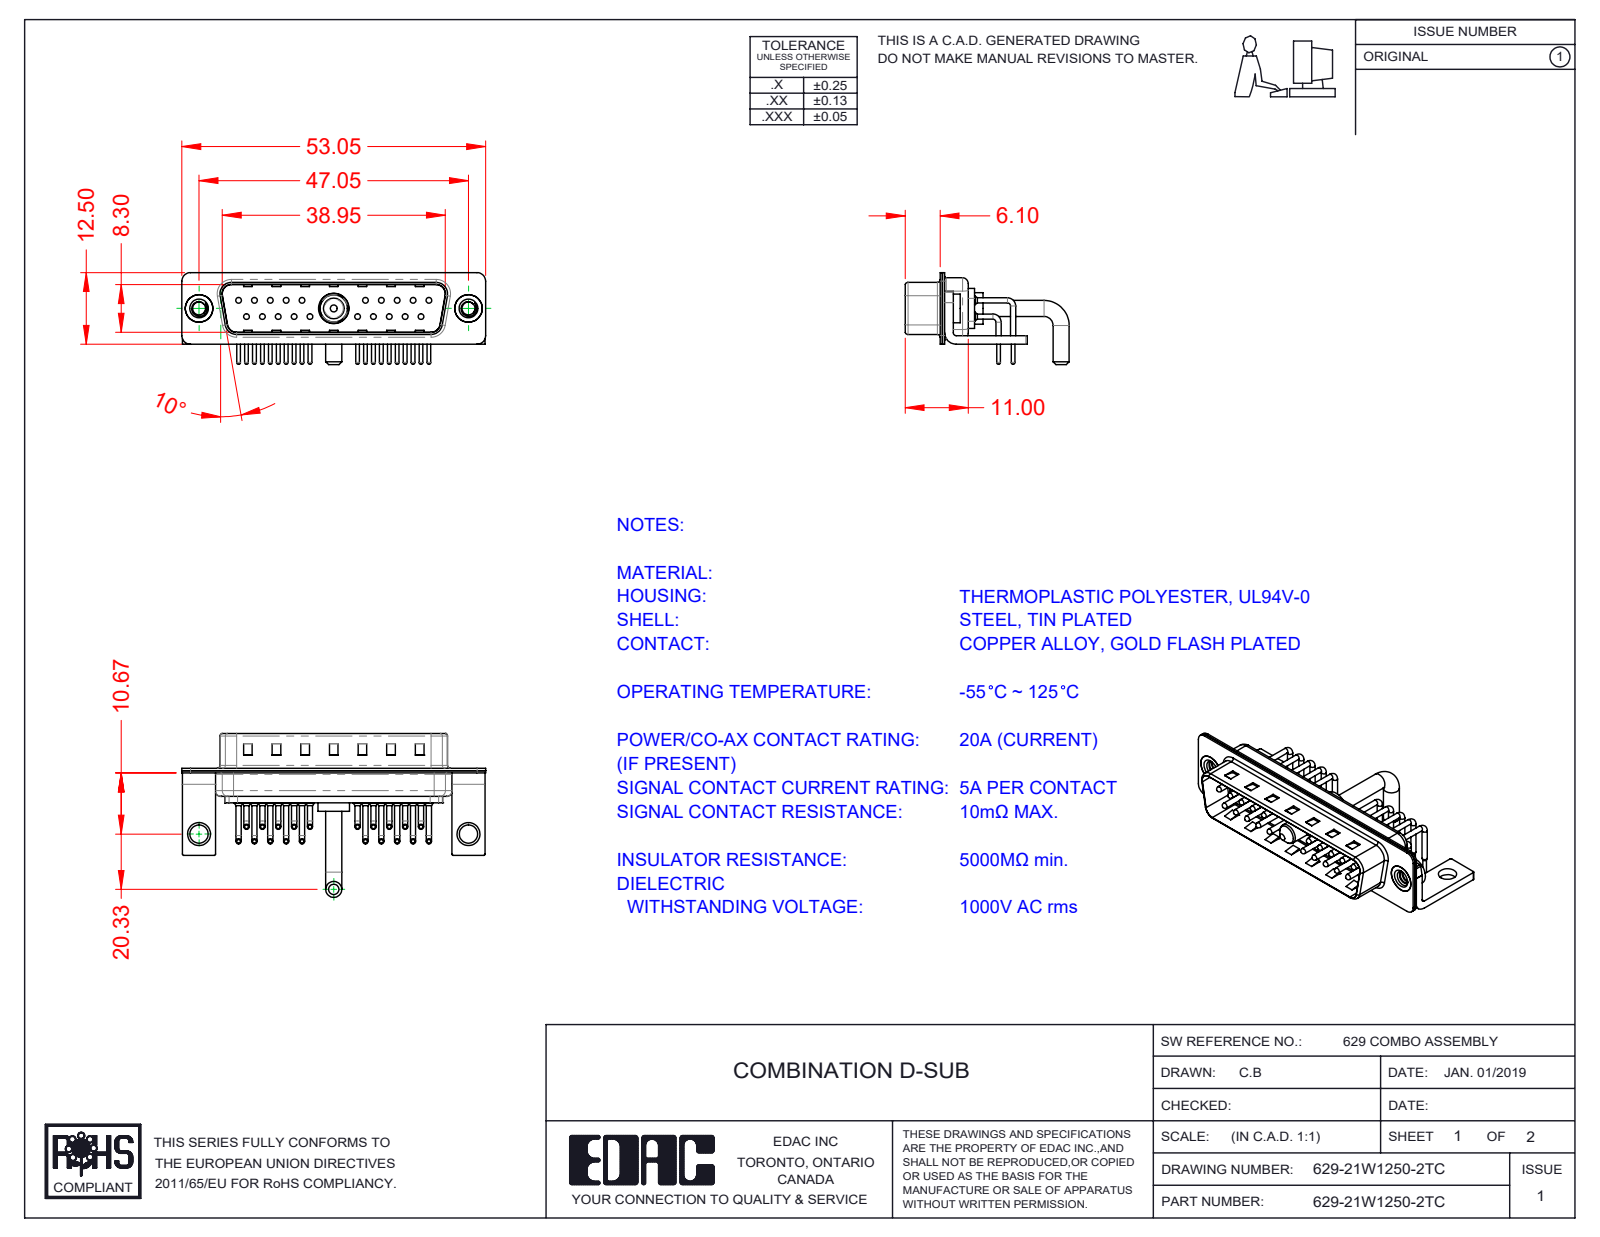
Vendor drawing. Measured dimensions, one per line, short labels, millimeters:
name: 629Combo Shell Front_25 Contacts; 629Combo Contact Row 1; 629Combo Shell Rear_25 Contacts; Power Pin_Ext 20A RA (+5 more)
written by: SolidWorks 2020 (CONFIG_CONTROL_DESIGN)
unit: mm
bodies: 29 solids, 2667 faces (1481 planar, 902 cylindrical, 284 other)
size: 53.05 × 28.63 × 16.05
volume: 3 373 mm³; area: 8 300 mm²
holes: 20× ⌀0.75, 20× ⌀1.6, 20× ⌀2, 2× ⌀2.26, 2× ⌀3.2, 2× ⌀4, 2× ⌀4.8, 1× ⌀4.85, 1× ⌀5.3
bosses: 40× ⌀0.9, 20× ⌀1.5, 20× ⌀1, 20× ⌀0.65, 2× ⌀5, 2× ⌀4.9, 2× ⌀2.8, 1× ⌀5.5
rounds: 20× R1.01, 16× R0.25, 16× R1.5, 13× R2, 9× R0.5, 8× R1.6, 4× R0.6, 4× R0.65
face distances: 0.4, 0.8, 9.5, 1.5, 9.1, 8.7, 9.9, 0.6, 1.2, 2.1
hole spacings: 3.16, 2.77, 5.54, 8.31, 5.04, 19.39, 20.97, 22.16
